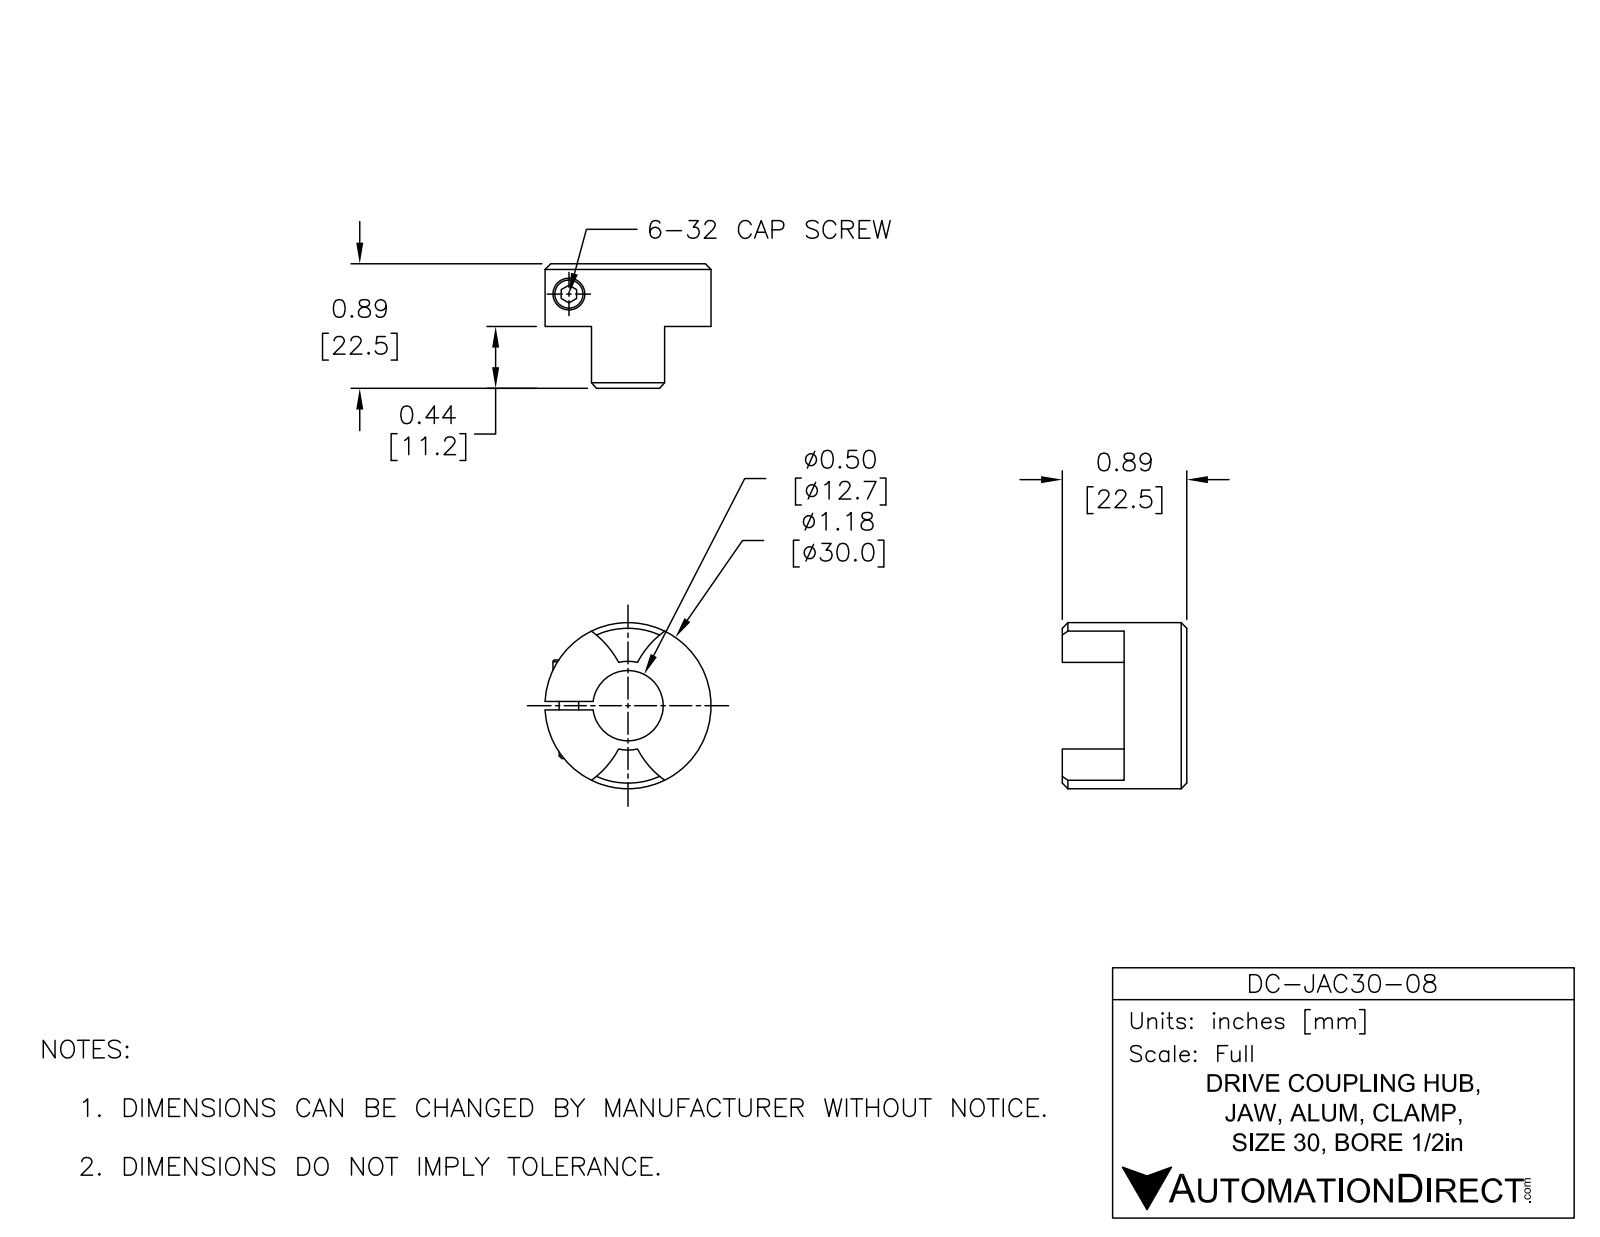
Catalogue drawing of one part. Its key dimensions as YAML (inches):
part_name: "DC-JAC30-08"
step_written_by: "SolidWorks 2015 (AUTOMOTIVE_DESIGN)"
units: inches
bodies: {solids: 1, faces: 27, planar: 7, cylindrical: 16, other: 4}
overall_size: [1.18, 1.179, 0.885]
volume: 0.442
surface_area: 5.659
round_holes:
  - {diameter: 0.154, count: 1}
  - {diameter: 0.25, count: 1}
  - {diameter: 0.5, count: 1}
round_bosses_or_shafts:
  - {diameter: 1.18, count: 1}
partial_cylinders:
  - {radius: 0.655, count: 2}
  - {radius: 0.315, count: 1}
face_to_face_distances: [0.445, 0.885, 0.44, 0.06, 0.217, 0.157]
